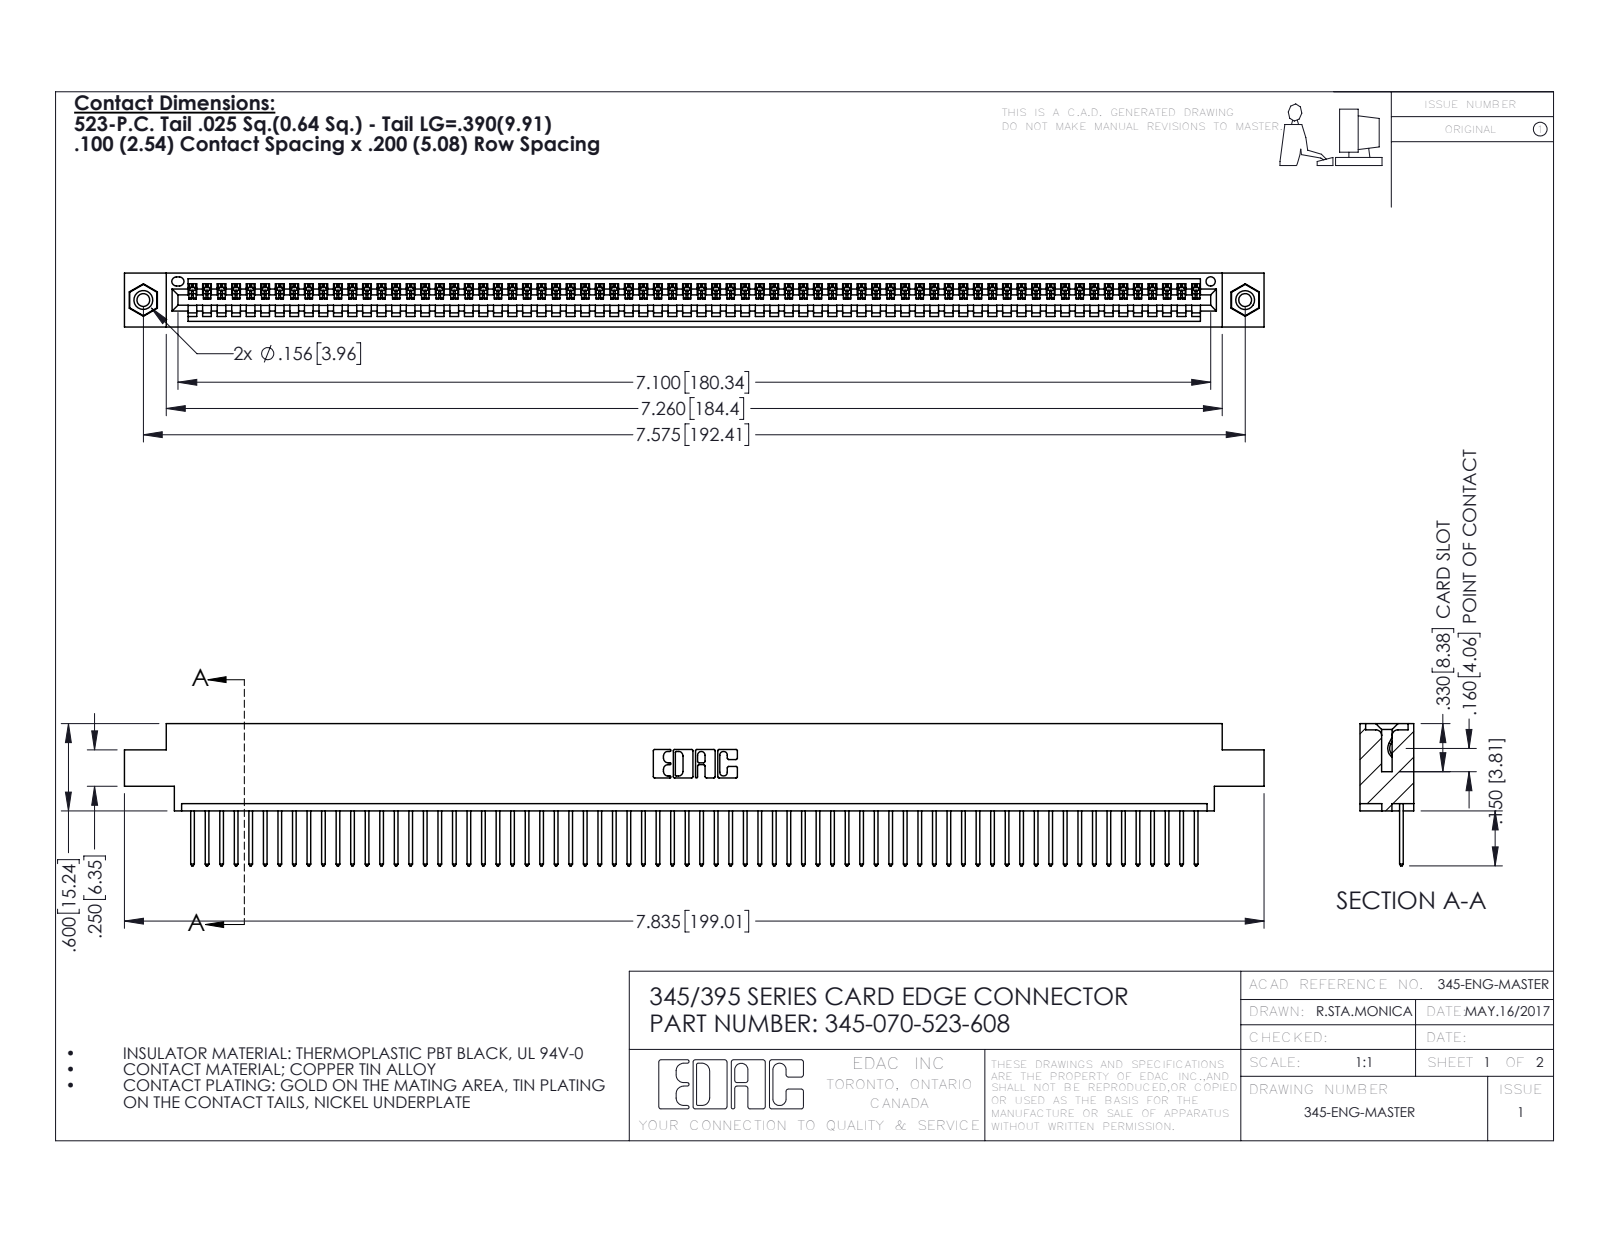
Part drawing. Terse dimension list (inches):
name: 345-250-001_345-250-003-102; 345-070-523-608; 345 Part_0.170 Offset - 0.156 Dia-TI; 345-292-001_345-293-123
written by: SolidWorks 2016 (CONFIG_CONTROL_DESIGN)
unit: in
bodies: 73 solids, 4250 faces (2916 planar, 1318 cylindrical, 16 other)
size: 7.835 × 0.977 × 0.37
volume: 1.159 in³; area: 40.04 in²
holes: 2× ⌀0.089, 2× ⌀0.125, 2× ⌀0.156, 1× ⌀0.064
bosses: 2× ⌀0.155
rounds: 140× R0.006, 140× R0.01, 22× R0.01, 6× R0.007, 6× R0.031, 3× R0.026, 2× R0.031, 2× R0.04
face distances: 0.072, 0.298, 0.37, 0.098, 0.272, 0.025, 0.2, 0.225, 0.175, 0.149
hole spacings: 0.27, 7.339, 7.575
